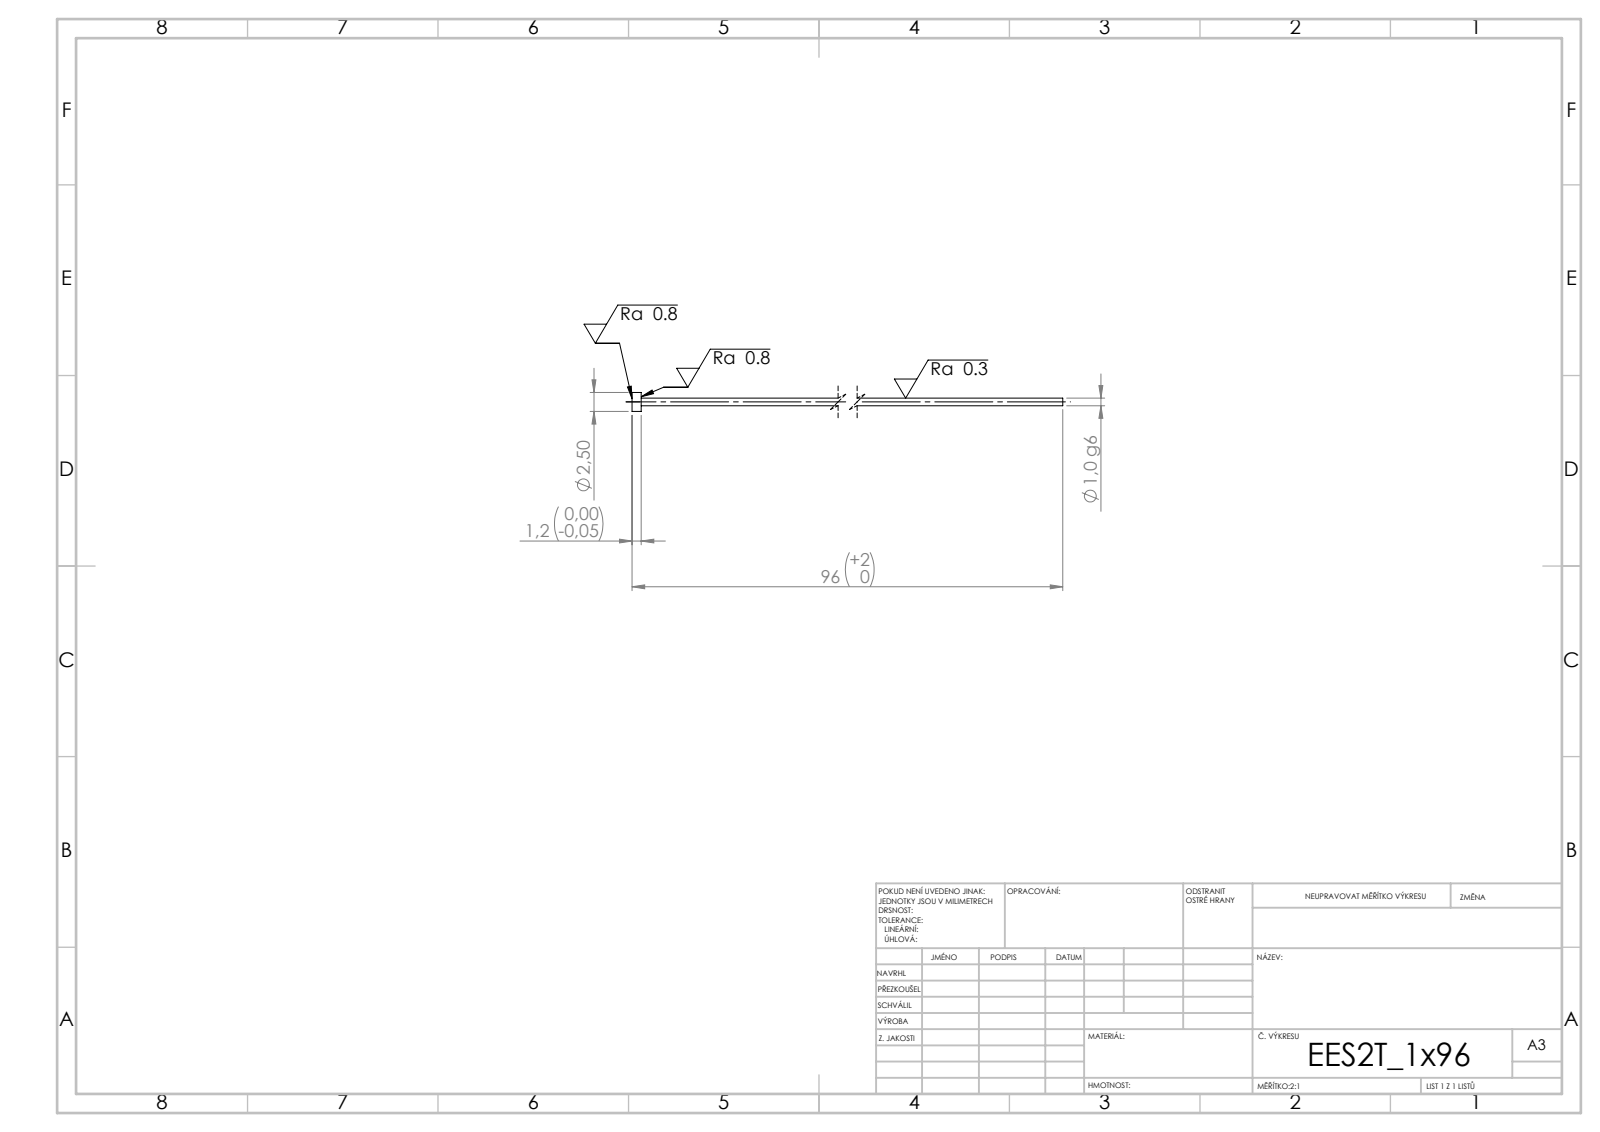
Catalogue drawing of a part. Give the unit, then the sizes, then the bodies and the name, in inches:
Units: inches
Overall size (bounding box): 3.78 × 0.098 × 0.098
Round bosses / shafts (diameter × count): ⌀0.098 ×1, ⌀0.039 ×1
Main face-to-face distances: 0.047, 3.78, 3.732
Volume: 0.005 in³ · Surface area: 0.491 in²
Bodies: 1 solid, 7 faces (3 planar, 4 cylindrical, 0 other)
STEP written by: SolidWorks 2019 (CONFIG_CONTROL_DESIGN)
